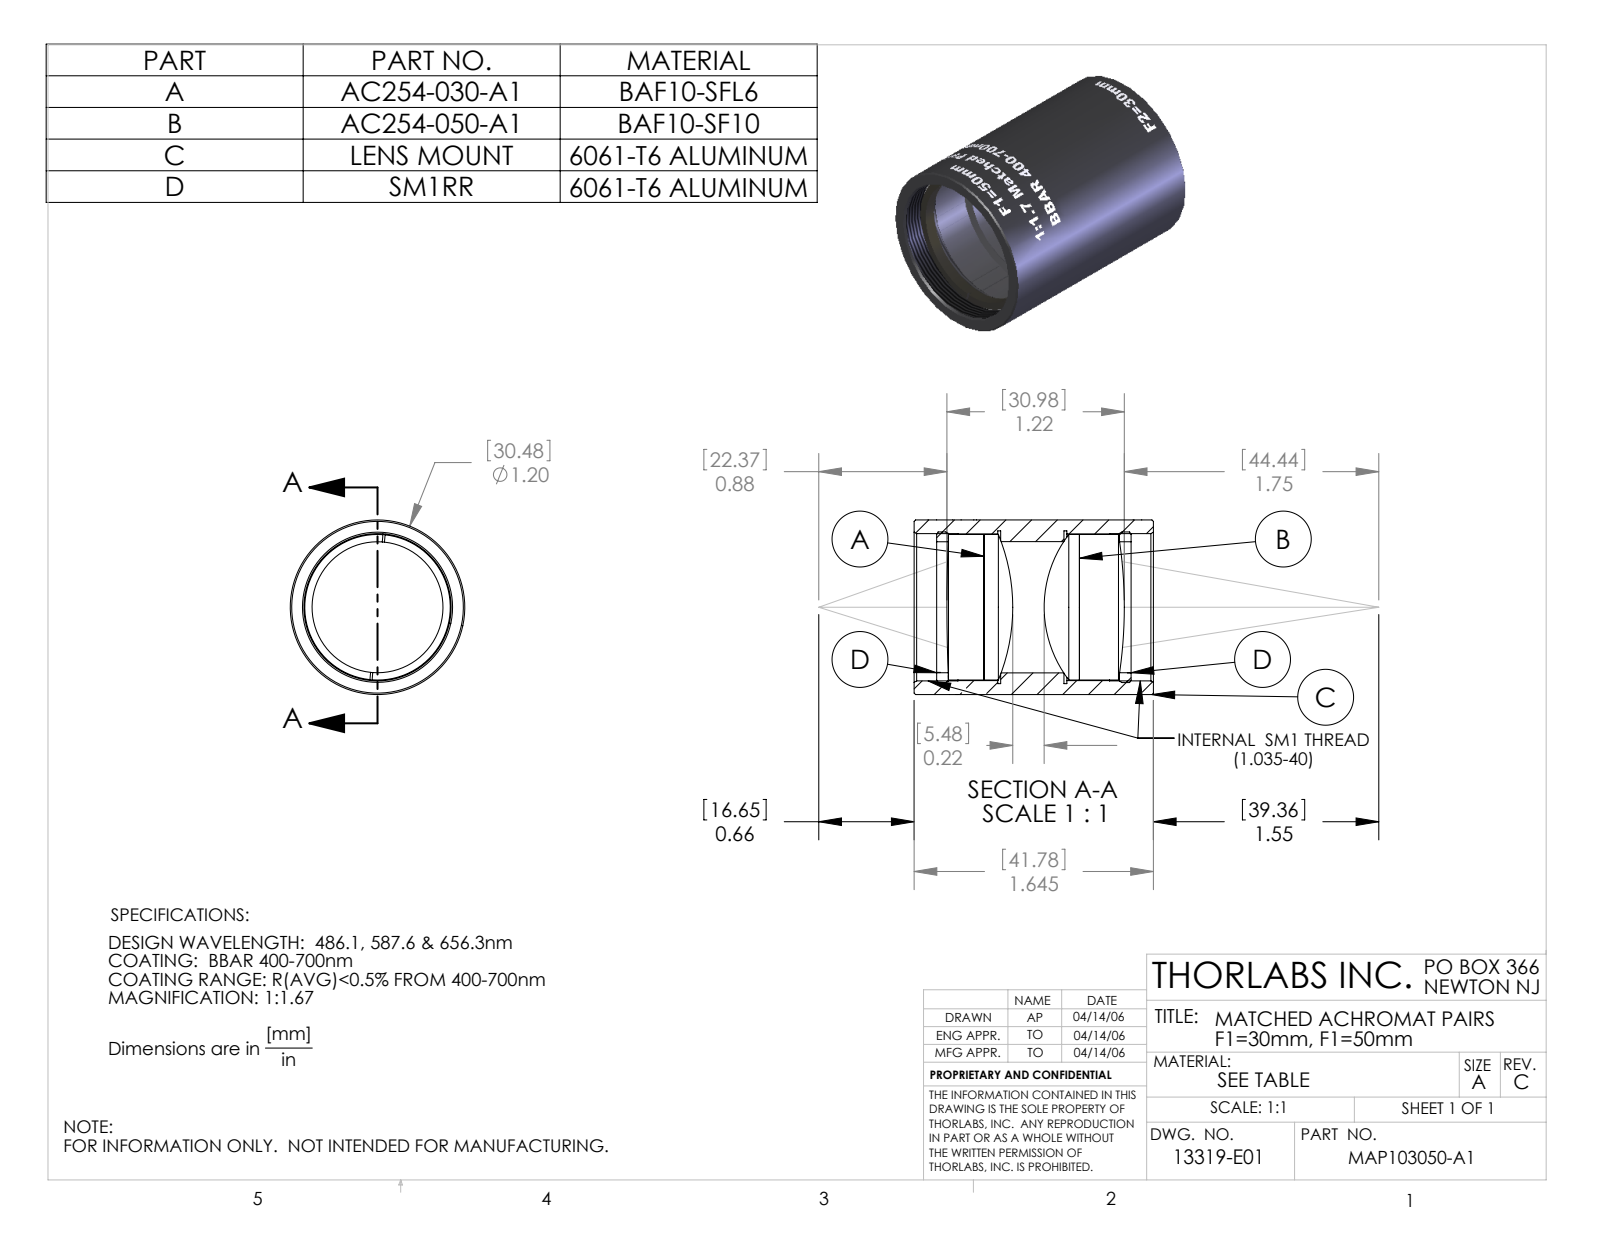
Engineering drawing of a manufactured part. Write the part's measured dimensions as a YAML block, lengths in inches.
part_name: "13319-E0W"
step_written_by: "SolidWorks 2007 (AUTOMOTIVE_DESIGN)"
units: inches
bodies: {solids: 0, faces: 143, planar: 18, cylindrical: 109, other: 16}
overall_size: [1.645, 1.2, 1.2]
round_holes:
  - {diameter: 0.9, count: 1}
  - {diameter: 1.012, count: 1}
round_bosses_or_shafts:
  - {diameter: 1.2, count: 1}
face_to_face_distances: [1.645, 1.49, 0.155, 0.154, 1.337, 1.491, 0.015, 1.465, 1.311, 0.025]
